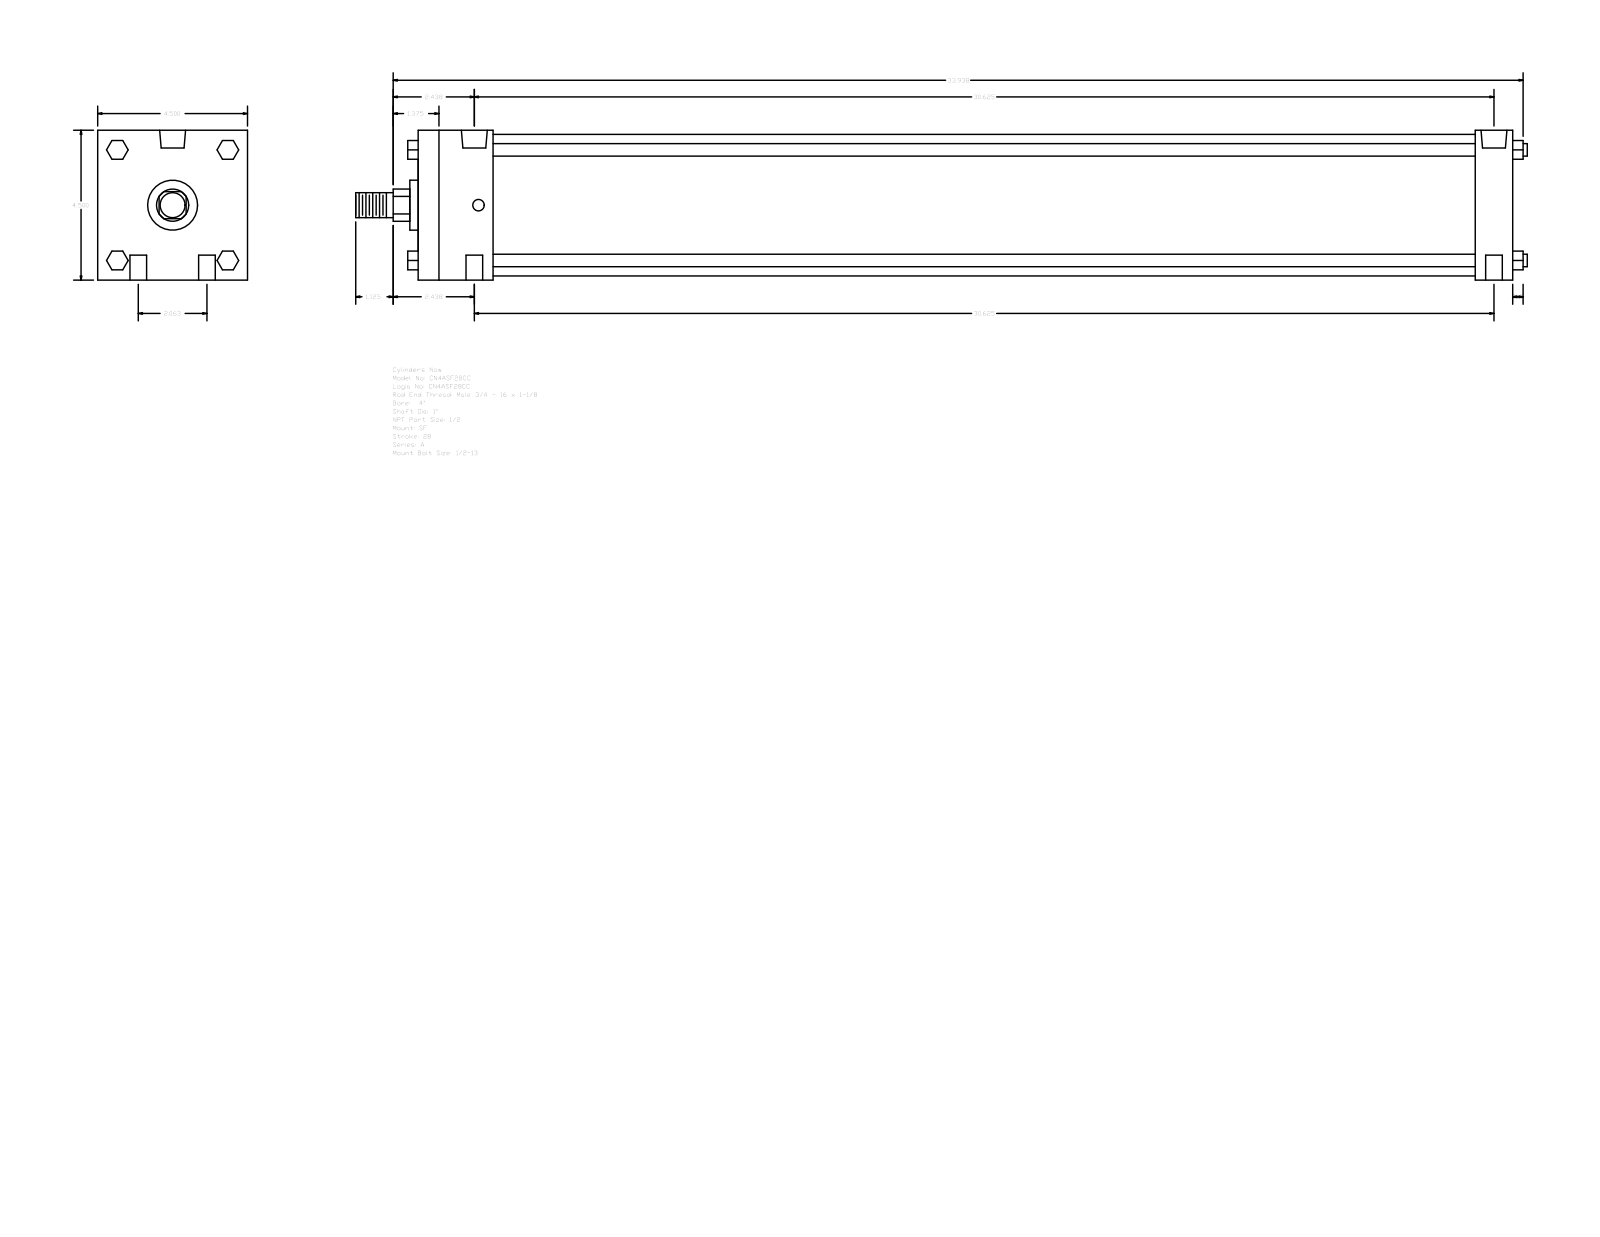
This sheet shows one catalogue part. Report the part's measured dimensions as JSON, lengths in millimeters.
{"part_name": "A_SF__0400_1", "step_written_by": "GSSL Pune (CONFIG_CONTROL_DESIGN)", "units": "millimeters", "bodies": {"solids": 0, "faces": 124, "planar": 94, "cylindrical": 30, "other": 0}, "overall_size": [893.76, 114.3, 114.3], "round_holes": [[12.7, 4], [8.73, 2], [19.77, 2]], "round_bosses_or_shafts": [[9.53, 4], [107.95, 1], [38.1, 1], [25.4, 1], [19.05, 1]], "partial_cylinders_radius": [[12.29, 1]], "face_to_face_distances": [114.3, 835.03, 806.45, 28.58, 57.15, 749.3, 777.88, 14.29, 42.16, 73.03], "hole_center_spacings": [26.19, 778.32, 777.88, 52.38, 779.64, 771.52]}
